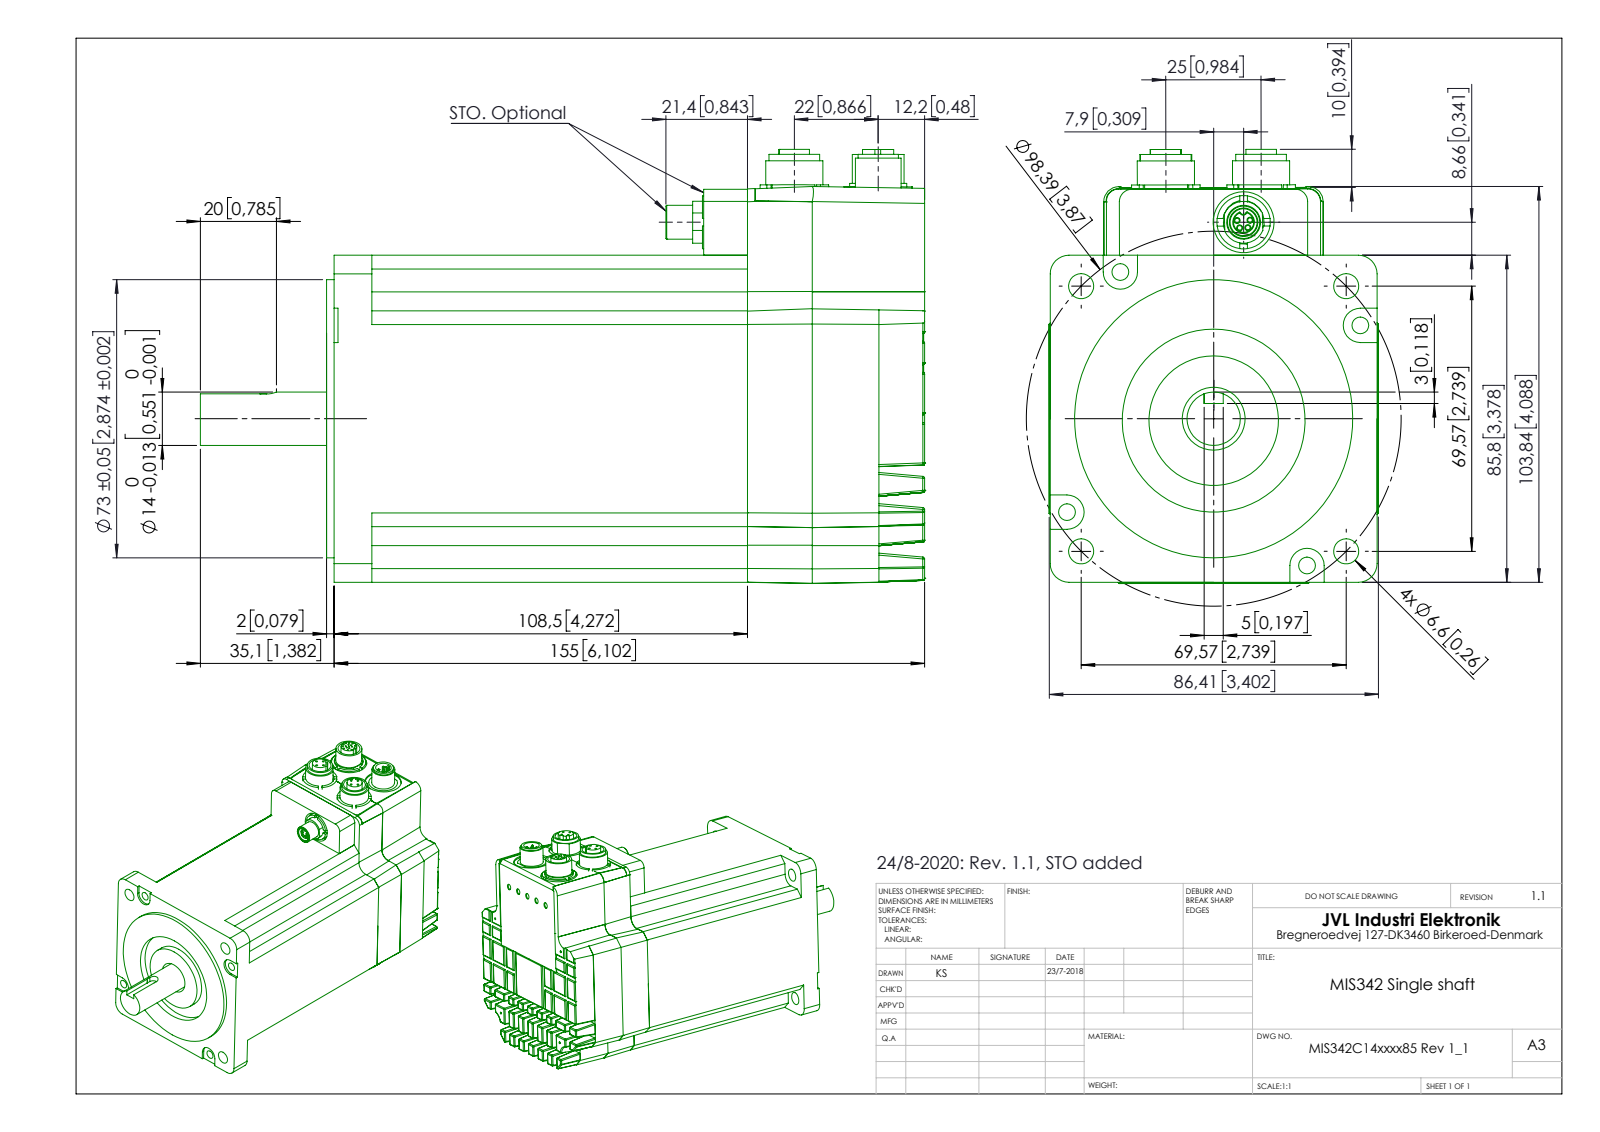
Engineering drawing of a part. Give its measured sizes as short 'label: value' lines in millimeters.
name: MIS342C14xxxx85 R1_1
written by: SolidWorks 2018 (AUTOMOTIVE_DESIGN)
unit: mm
bodies: 2 solids, 1320 faces (552 planar, 576 cylindrical, 192 other)
size: 190.1 × 113.9 × 86.45
volume: 1 052 000 mm³; area: 115 437 mm²
holes: 17× ⌀0.7, 12× ⌀1, 5× ⌀3, 4× ⌀1.2, 4× ⌀4.3, 4× ⌀4.4, 4× ⌀6.6, 3× ⌀11.5, 2× ⌀16, 2× ⌀19, 1× ⌀7.1, 1× ⌀8.2
bosses: 5× ⌀1, 3× ⌀18, 3× ⌀15, 3× ⌀8.2, 2× ⌀14, 2× ⌀13.3, 2× ⌀8, 1× ⌀73
rounds: 191× R0.5, 4× R0.2, 4× R4.5, 4× R4.9, 4× R5, 4× R9.5, 3× R0.48, 3× R2
face distances: 85.8, 14.6, 0.6, 71.2, 110.5, 111.1, 2, 108.5, 109.1, 157
hole spacings: 3.25, 3.54, 1.65, 1.67, 2.48, 8.4, 25.04, 45.63
